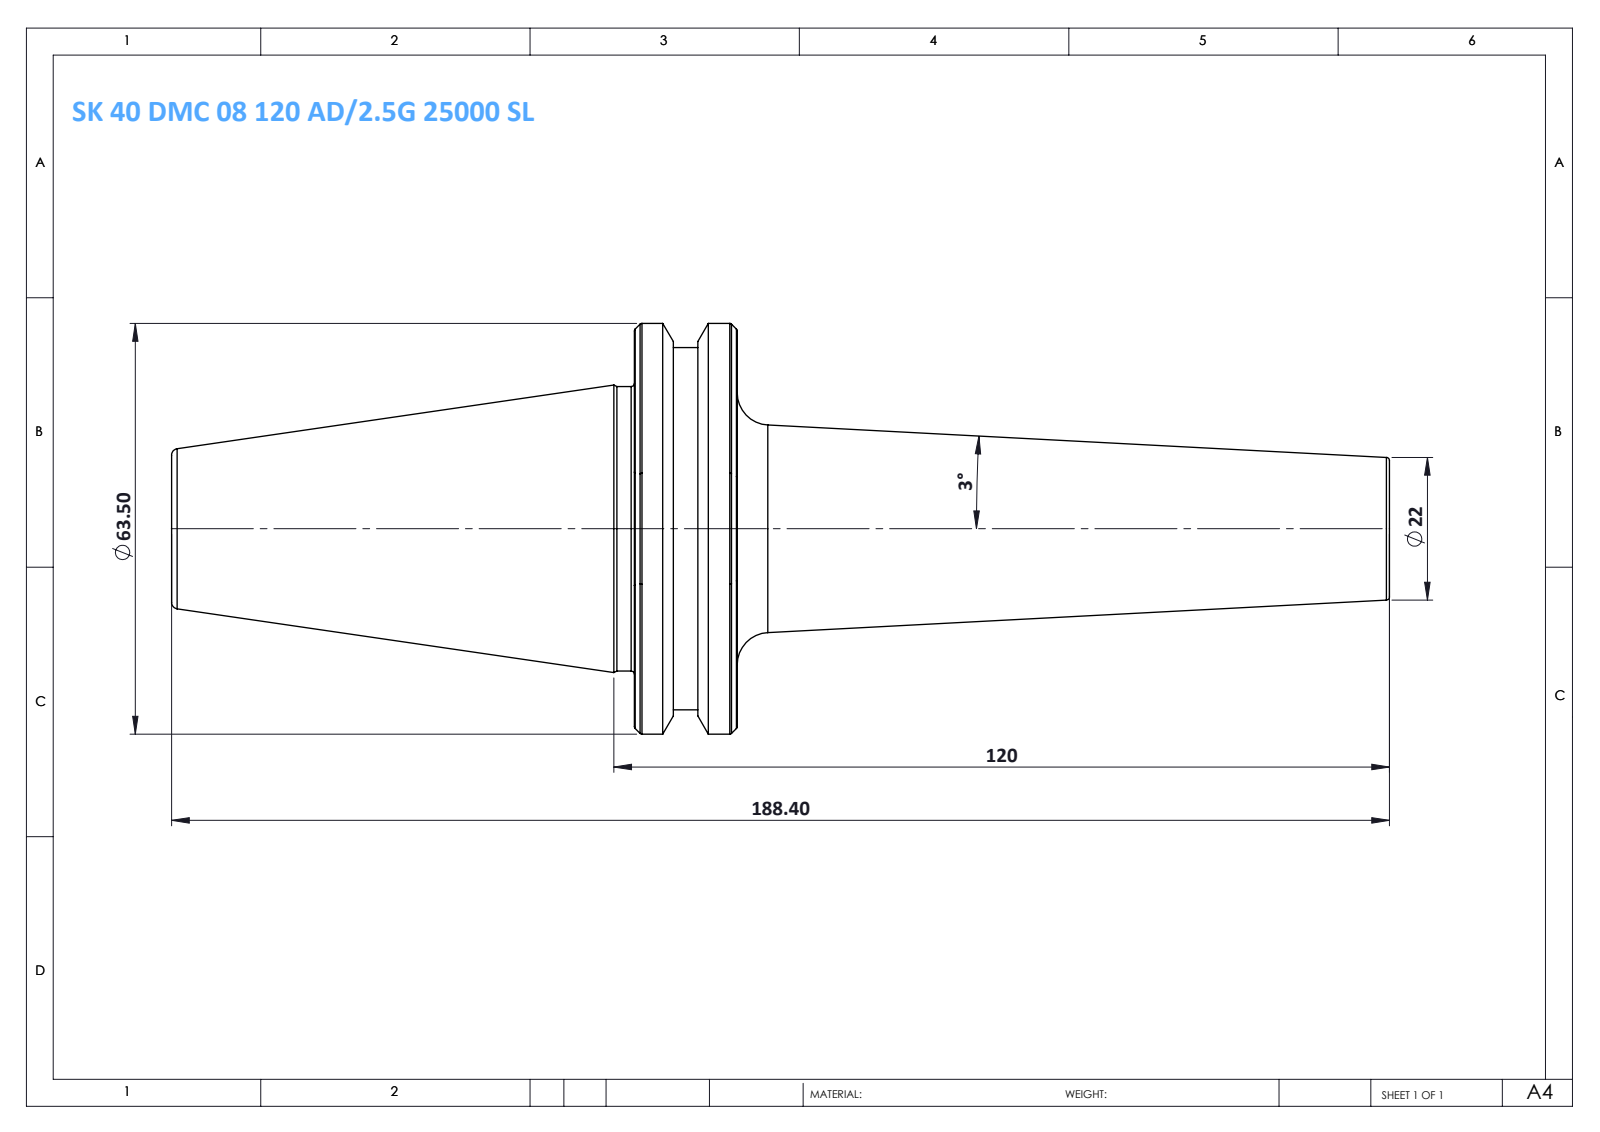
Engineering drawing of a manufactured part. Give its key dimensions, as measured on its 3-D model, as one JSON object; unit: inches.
{"part_name": "SK 40 DMC 08 120 AD-2.5G 25000 SL", "step_written_by": "SolidWorks 2014 (CONFIG_CONTROL_DESIGN)", "units": "inches", "bodies": {"solids": 1, "faces": 64, "planar": 6, "cylindrical": 8, "other": 50}, "overall_size": [7.417, 2.5, 2.5], "volume_in3": 10.82, "surface_area_in2": 38.66, "round_bosses_or_shafts": [[2.5, 1], [2.205, 1], [1.732, 1]], "face_to_face_distances": [0.626, 3.445, 2.819, 3.972, 4.598, 7.417, 4.362, 0.39, 0.236, 3.055]}
